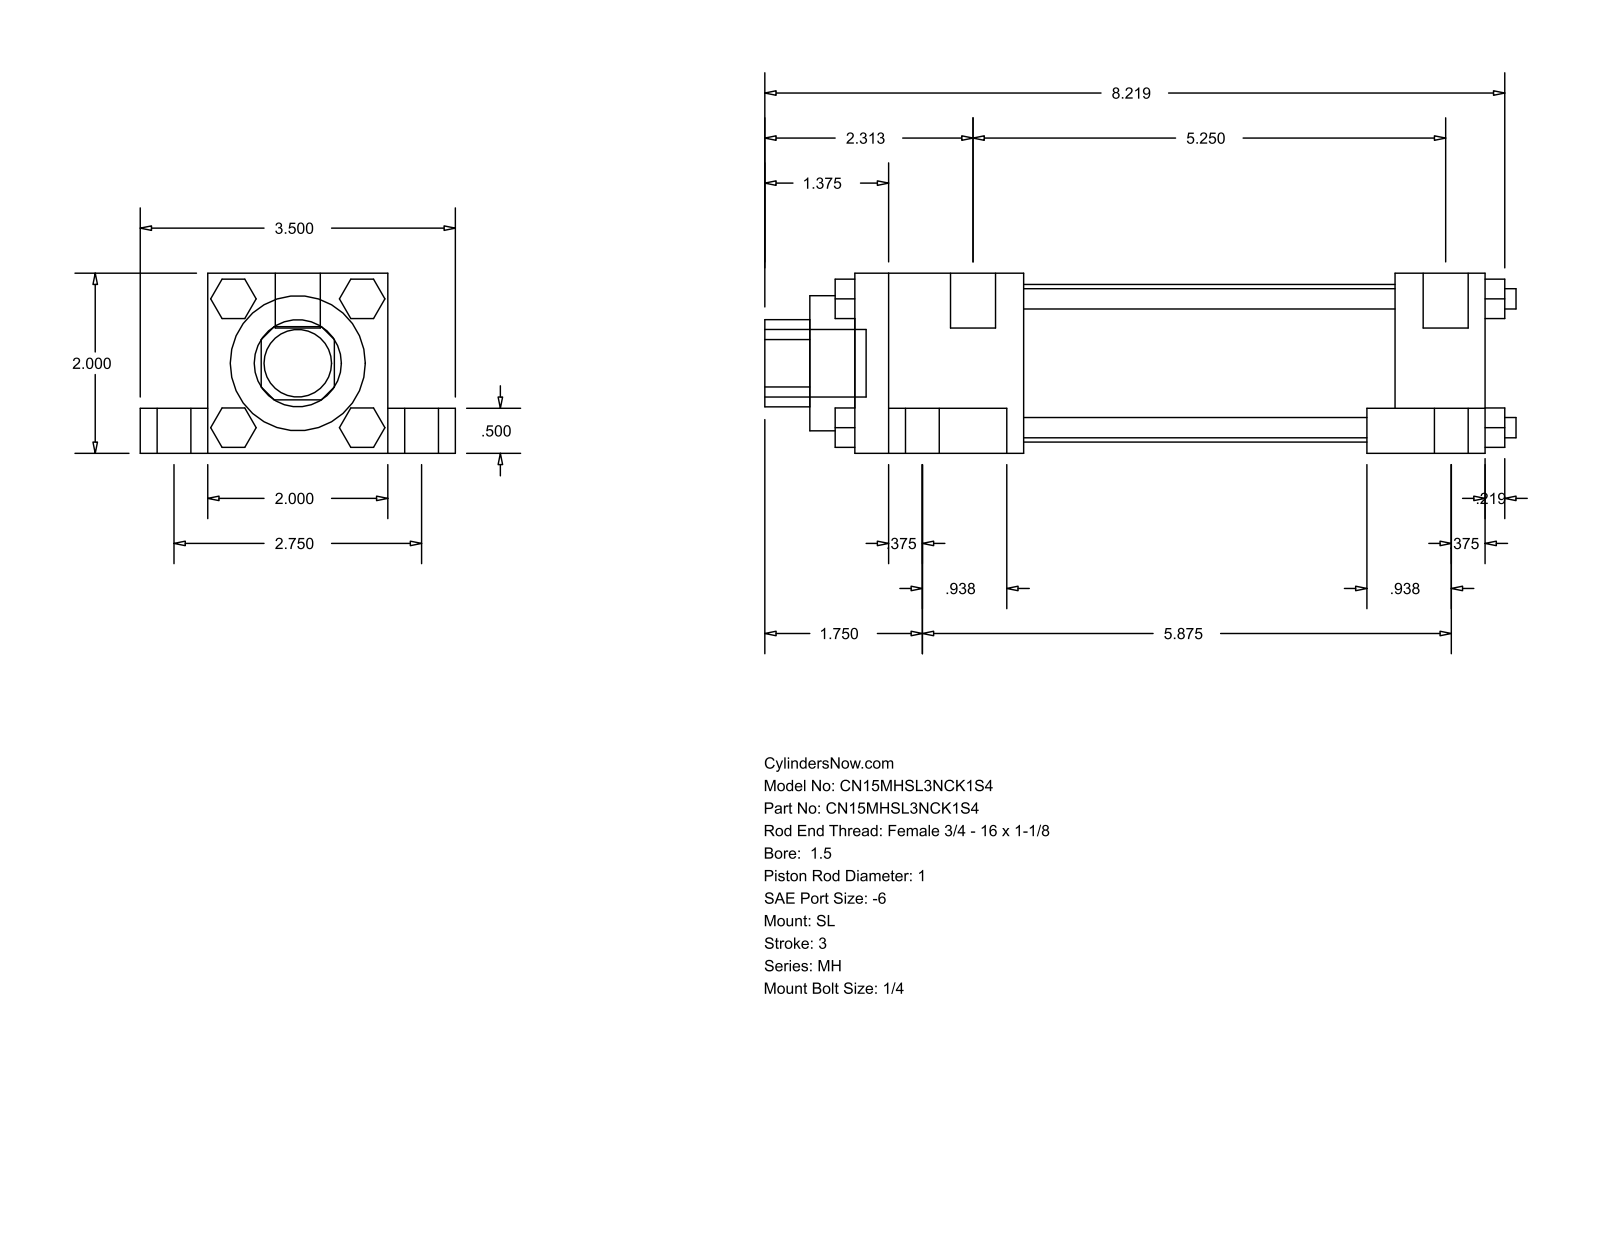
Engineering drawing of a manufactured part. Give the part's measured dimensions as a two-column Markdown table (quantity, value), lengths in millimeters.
| quantity | value |
| --- | --- |
| part name | MH_SL__0150_1 |
| STEP written by | GSSL Pune (CONFIG_CONTROL_DESIGN) |
| units | millimeters |
| bodies | 0 solids, 148 faces (112 planar, 36 cylindrical, 0 other) |
| overall size | 211.93 × 88.9 × 50.8 |
| round holes (diameter × count) | 25.4 × 1, 38.1 × 1, 44.45 × 1 |
| round bosses / shafts (diameter × count) | 15.88 × 4, 9.53 × 4, 5.71 × 4, 5.56 × 4, 12.7 × 2, 19.05 × 1 |
| partial cylindrical surfaces (radius × count) | 12.29 × 1 |
| main face-to-face distances | 50.8, 12.7, 38.1, 19.05, 69.85, 177.8, 25.4, 9.52, 33.34, 134.94 |
